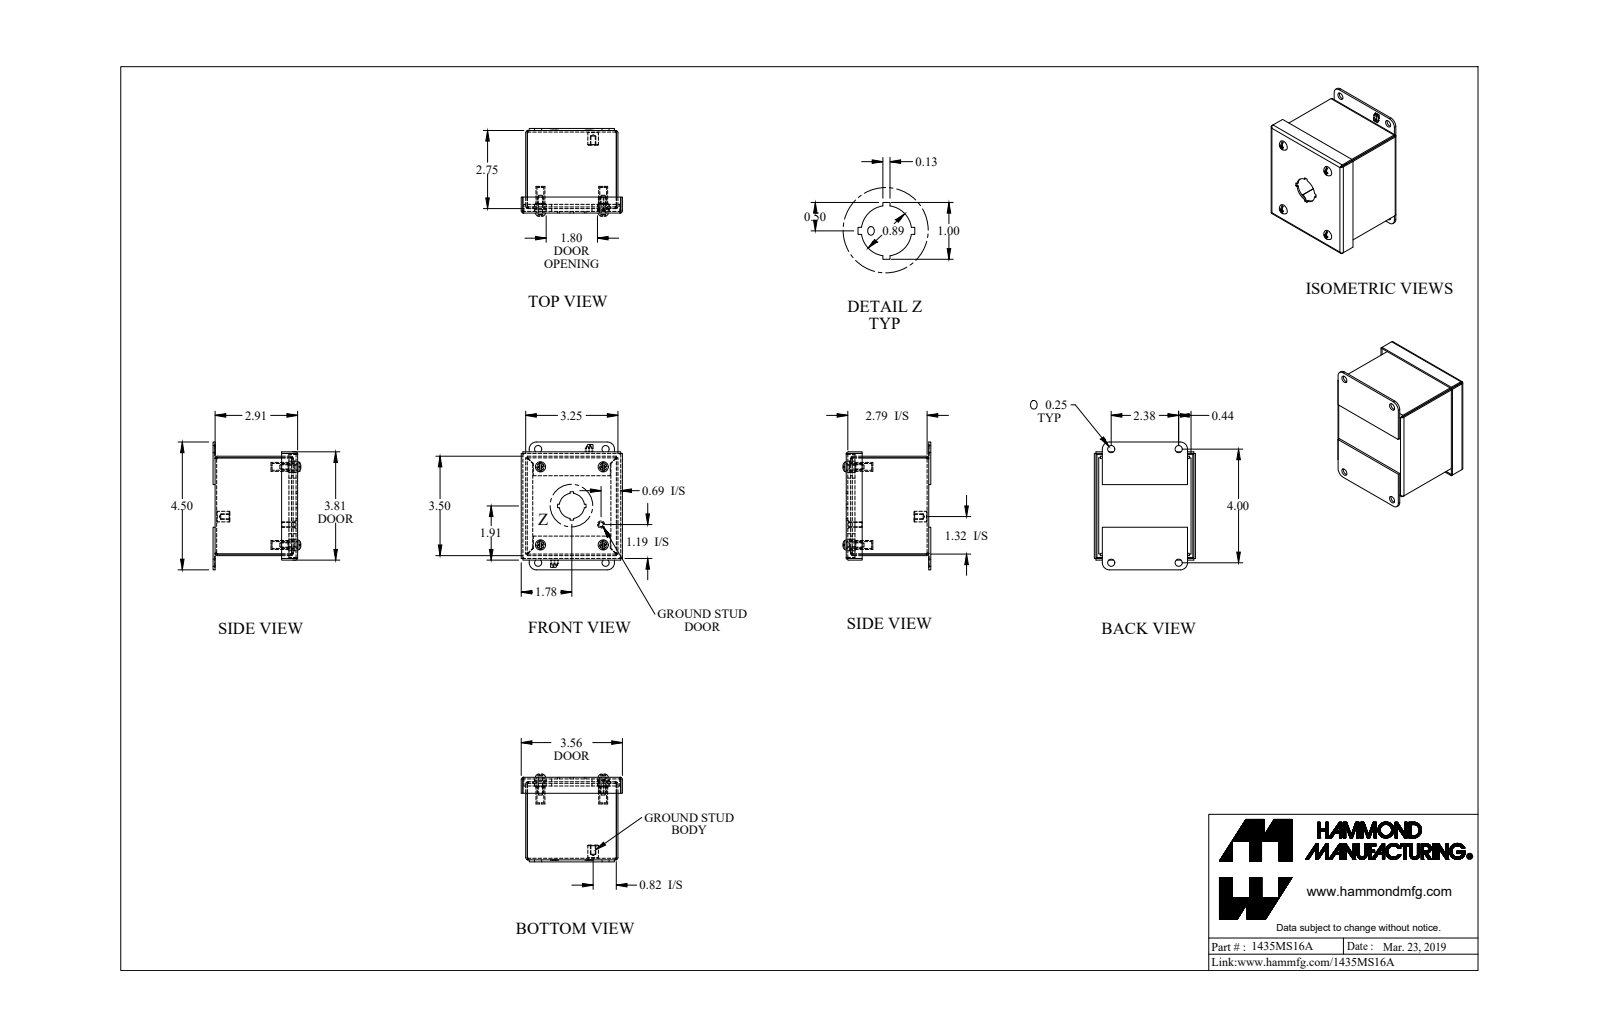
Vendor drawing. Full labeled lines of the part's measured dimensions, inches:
Part name (STEP PRODUCT): 1435MS16A_Default
STEP written by: SolidWorks 2019 (CONFIG_CONTROL_DESIGN)
Units: inches
Bodies: 19 solids, 461 faces (295 planar, 136 cylindrical, 30 other)
Overall size (bounding box): 4.5 × 3.562 × 3.089
Volume: 6.205 in³ · Surface area: 191.7 in²
Round holes (diameter × count): ⌀0.25 ×8, ⌀0.065 ×4, ⌀0.239 ×4, ⌀0.253 ×4, ⌀0.406 ×4, ⌀0.156 ×1, ⌀0.886 ×1
Round bosses / shafts (diameter × count): ⌀0.19 ×5, ⌀0.406 ×4, ⌀0.315 ×4, ⌀0.148 ×4, ⌀0.375 ×1, ⌀0.25 ×1
Partial cylindrical surfaces — rounded edges, fillets, slot ends (radius × count): R0.029 ×12, R0.086 ×12, R0.171 ×4, R0.25 ×4, R0.125 ×2
Main face-to-face distances: 0.057, 2.85, 0.057, 3.193, 3.443, 2.907, 2.793, 0.156, 2.979, 2.922
Hole centre spacings: 0.63, 2.211, 2.75, 3.529, 4.08, 2.212, 1.763, 2.377
